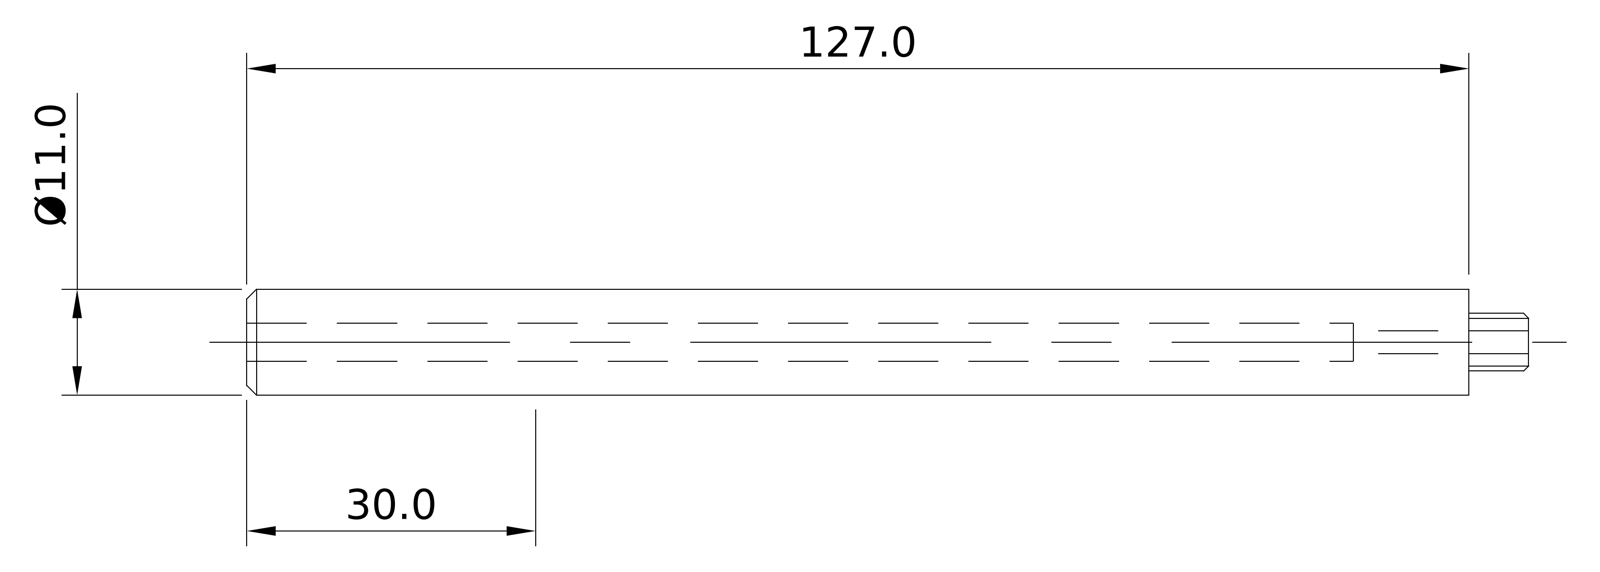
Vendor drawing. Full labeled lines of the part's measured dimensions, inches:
STEP written by: ACIS (automotive_design)
Units: inches
Bodies: 1 solid, 19 faces (3 planar, 8 cylindrical, 8 other)
Overall size (bounding box): 5.236 × 0.433 × 0.433
Volume: 0.649 in³ · Surface area: 9.728 in²
Round holes (diameter × count): ⌀0.087 ×1, ⌀0.157 ×1
Round bosses / shafts (diameter × count): ⌀0.433 ×1, ⌀0.236 ×1
Main face-to-face distances: 5, 0.236, 5.236
